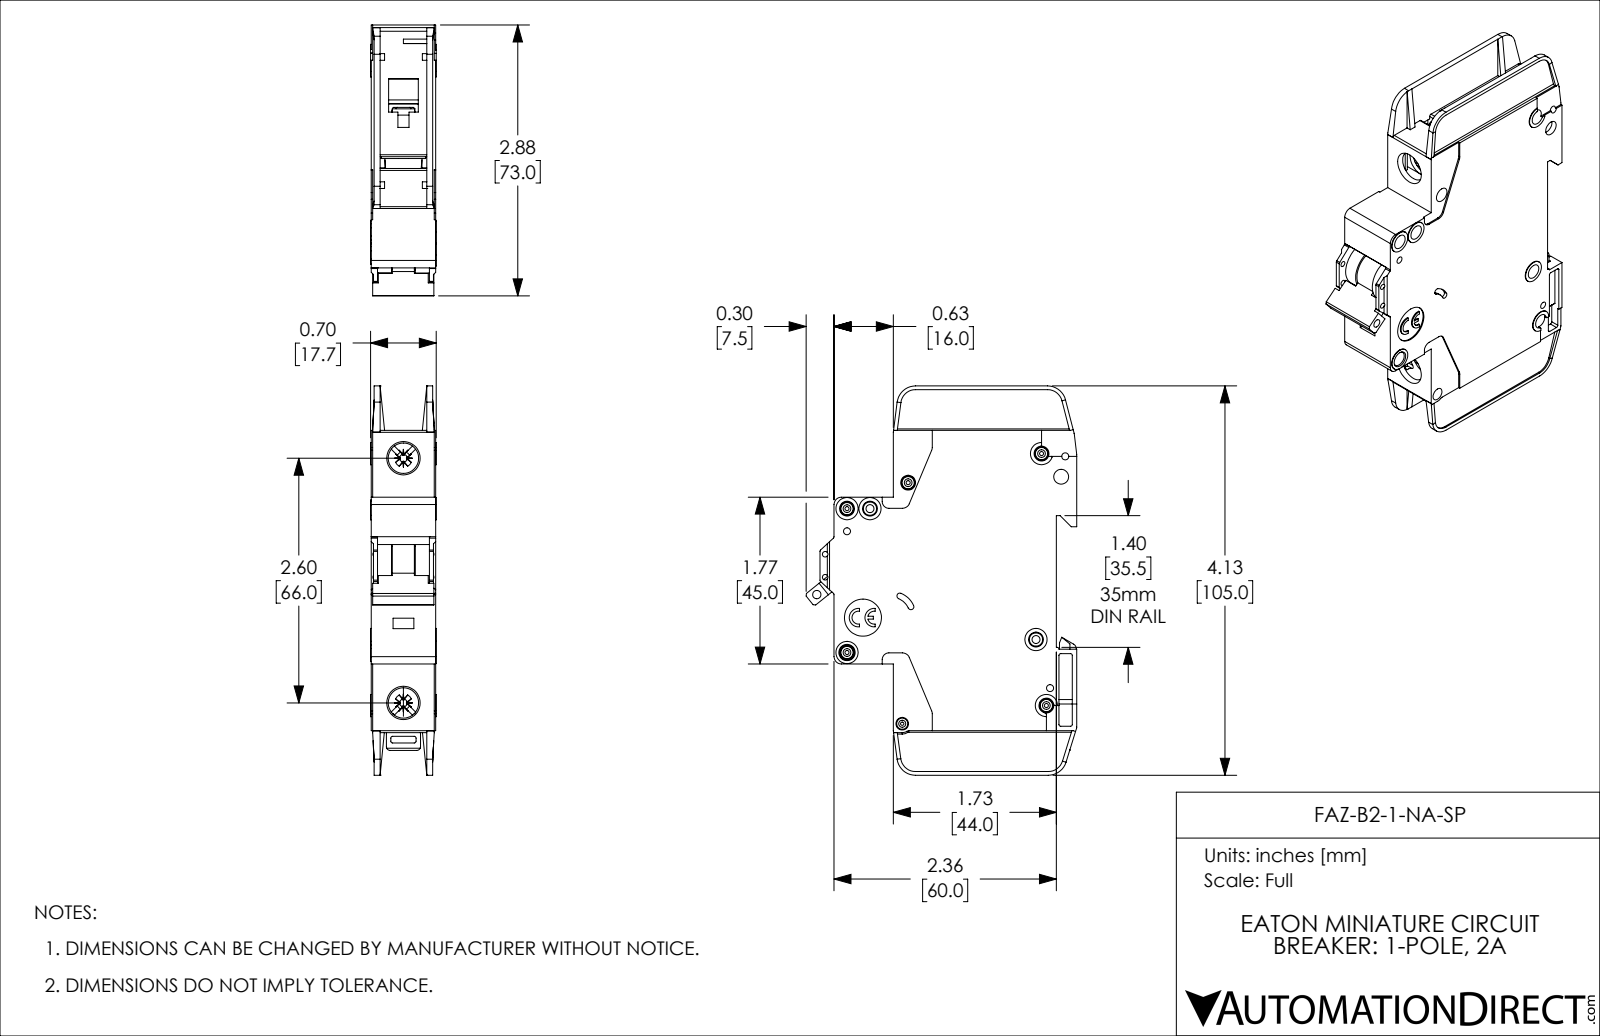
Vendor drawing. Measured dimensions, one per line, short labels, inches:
name: FAZ-B2-1-NA-SP
written by: SolidWorks 2019 (AUTOMOTIVE_DESIGN)
unit: in
bodies: 1 solid, 1127 faces (671 planar, 357 cylindrical, 99 other)
size: 4.134 × 2.876 × 0.697
volume: 4.682 in³; area: 41.01 in²
holes: 8× ⌀0.157, 5× ⌀0.043, 4× ⌀0.075, 2× ⌀0.059, 2× ⌀0.085, 2× ⌀0.323, 1× ⌀0.035, 1× ⌀0.089, 1× ⌀0.098, 1× ⌀0.134, 1× ⌀0.394
bosses: 5× ⌀0.13, 4× ⌀0.236, 2× ⌀0.118, 1× ⌀0.098
rounds: 42× R0.02, 10× R0.016, 10× R0.039, 8× R0.079, 5× R0.197, 4× R0.008, 4× R0.026, 4× R0.043
face distances: 0.047, 0.685, 0.591, 0.638, 0.094, 0.543, 0.016, 0.031, 0.496, 0.575
hole spacings: 0.244, 0.537, 0.87, 0.189, 0.199, 0.204, 0.221, 0.24
